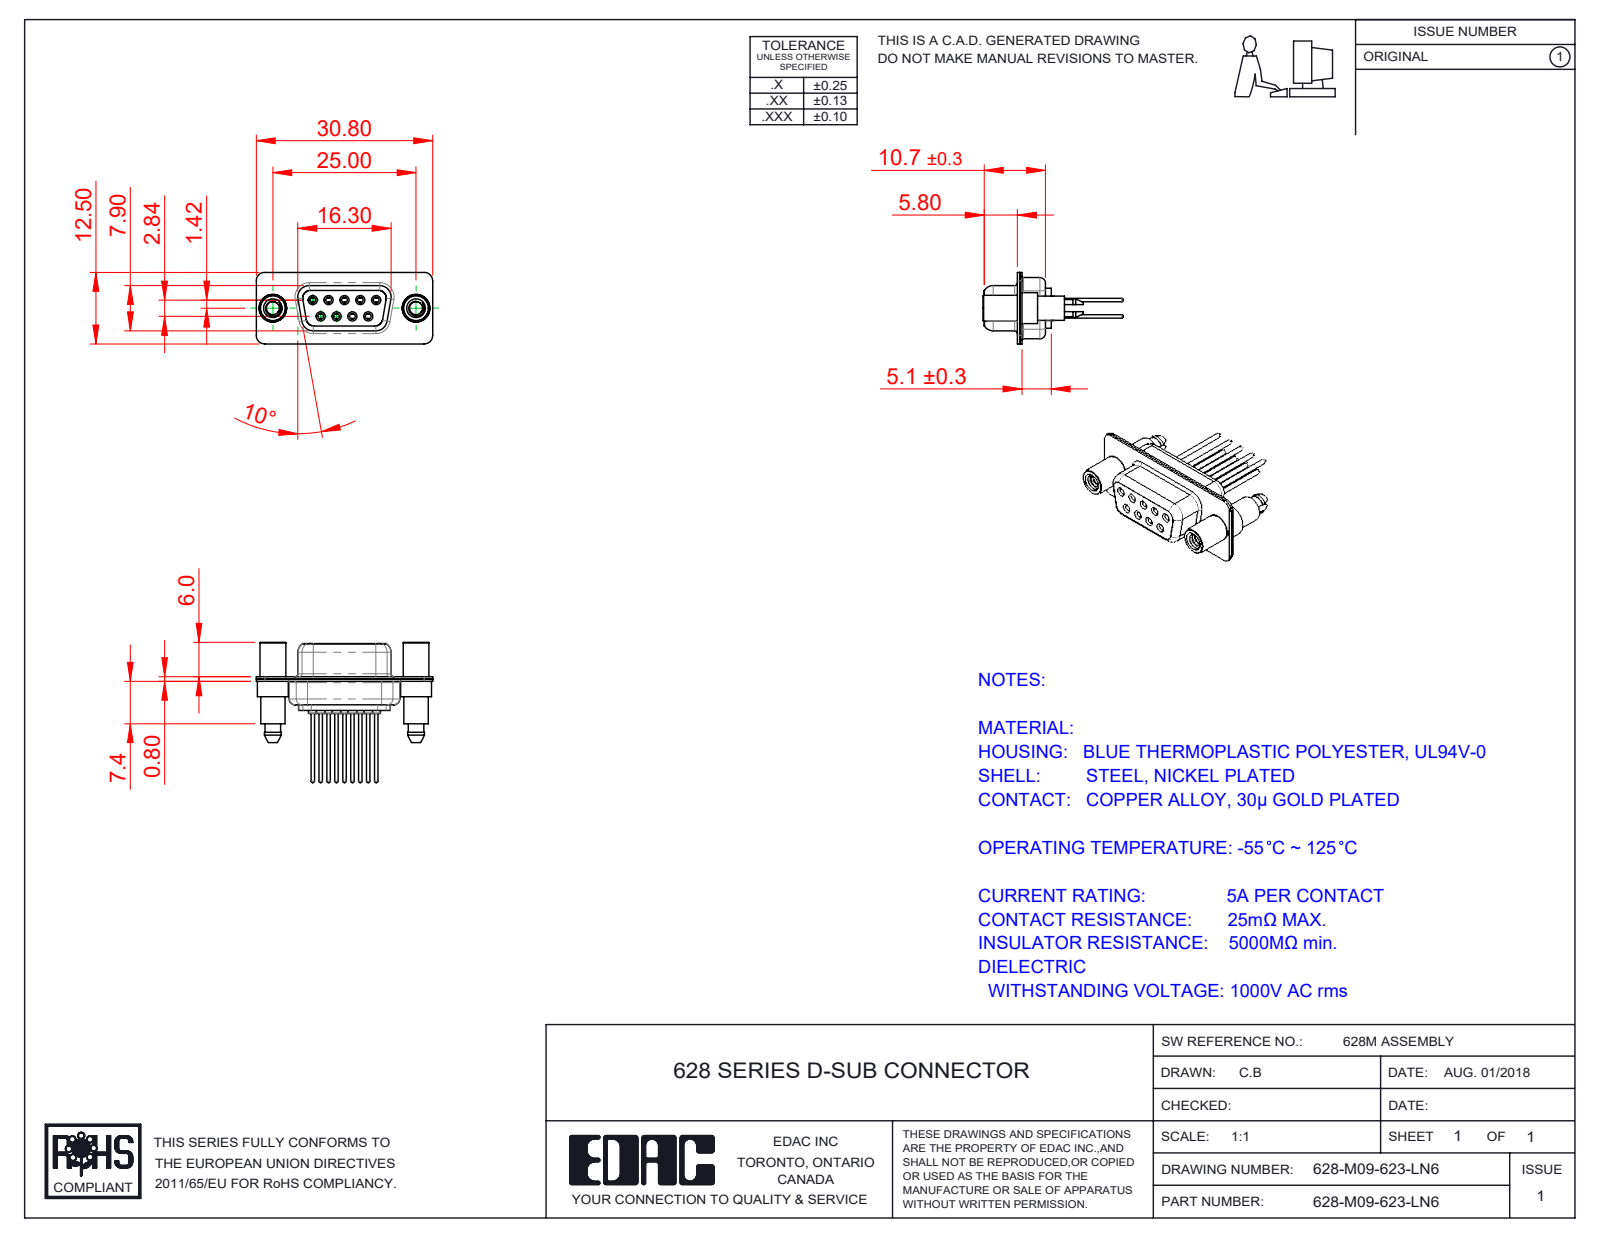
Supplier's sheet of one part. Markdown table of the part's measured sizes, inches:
| quantity | value |
| --- | --- |
| part name | 628-M09-623-LN6; 628M Shell Front_09 Contacts; 628M 4-40 Threaded Standoff and Boardlock; 628M Housing_09 Contacts (+3 more) |
| STEP written by | SolidWorks 2020 (CONFIG_CONTROL_DESIGN) |
| units | inches |
| bodies | 14 solids, 826 faces (220 planar, 336 cylindrical, 270 other) |
| overall size | 1.213 × 0.963 × 0.492 |
| volume | 0.126 in³ |
| surface area | 7.756 in² |
| round holes (diameter × count) | 0.039 × 9, 0.043 × 9, 0.067 × 9, 0.071 × 9, 0.079 × 9, 0.089 × 2, 0.157 × 2, 0.189 × 2 |
| round bosses / shafts (diameter × count) | 0.087 × 9, 0.063 × 9, 0.059 × 9, 0.024 × 9, 0.213 × 2, 0.193 × 2, 0.177 × 2, 0.167 × 2 |
| partial cylindrical surfaces (radius × count) | 0.059 × 18, 0.079 × 12, 0.063 × 10, 0.053 × 8, 0.01 × 4, 0.02 × 4, 0.024 × 4, 0.026 × 4 |
| main face-to-face distances | 0.016, 0.055, 0.018, 0.333, 0.031, 0.071, 0.039, 0.35, 0.244, 0.366 |
| hole center spacings | 0.124, 0.109, 0.218, 0.198, 0.198, 0.327, 0.28, 0.294 |
